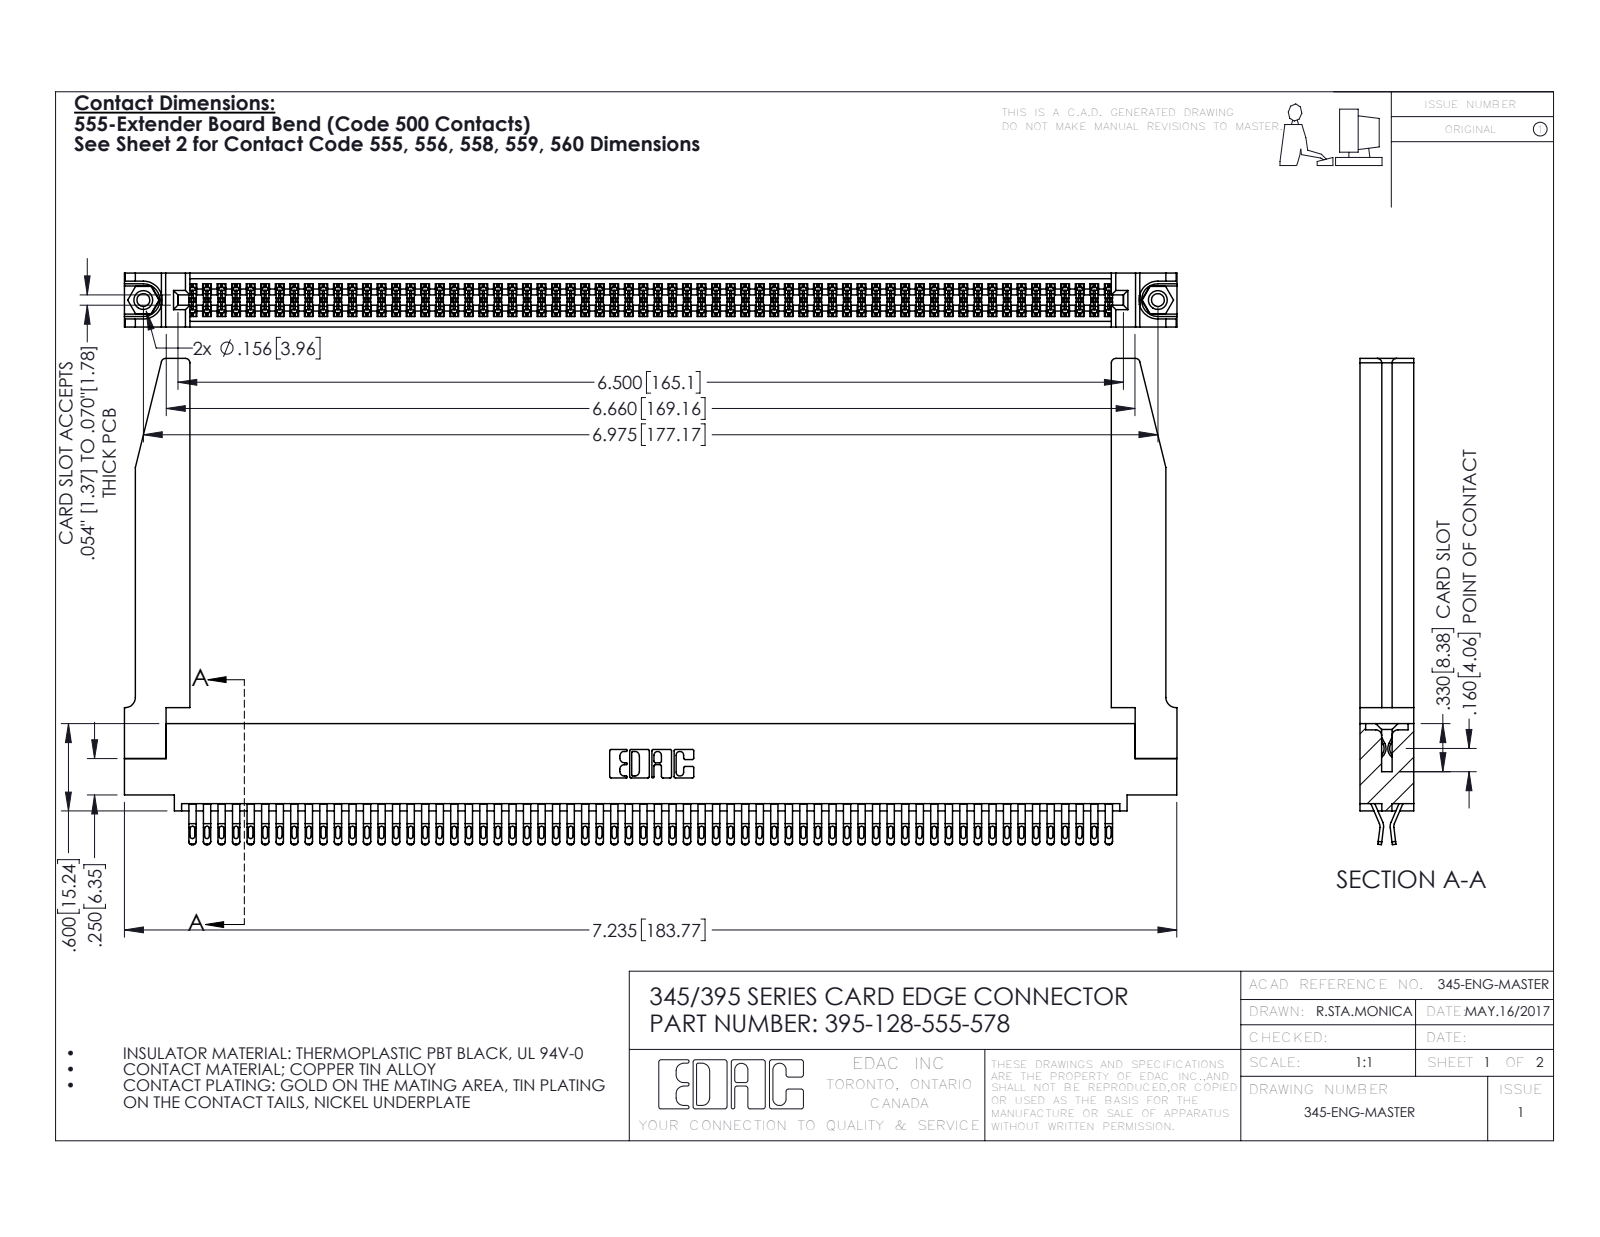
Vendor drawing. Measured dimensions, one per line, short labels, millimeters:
name: 345 Part_0.110 Offset - 0.156 Dia-TH; 345-250-001_345-250-001-102; 395-128-555-578; 345-220-078_345-220-078 (+1 more)
written by: SolidWorks 2016 (CONFIG_CONTROL_DESIGN)
unit: mm
bodies: 133 solids, 7532 faces (4194 planar, 3286 cylindrical, 52 other)
size: 183.8 × 84.9 × 9.4
volume: 26 120 mm³; area: 35 780 mm²
holes: 2× ⌀2.3, 2× ⌀3.2, 2× ⌀4, 1× ⌀1.6
bosses: 2× ⌀3.9
rounds: 320× R0.4, 256× R0.5, 192× R0.2, 22× R0.3, 8× R0.8, 6× R0.2, 6× R0.8, 3× R0.7
face distances: 1.8, 7.6, 9.4, 0.6, 2.5, 6.9, 5.1, 5.7, 4.4, 3.8
hole spacings: 6.9, 171.2, 177.2
